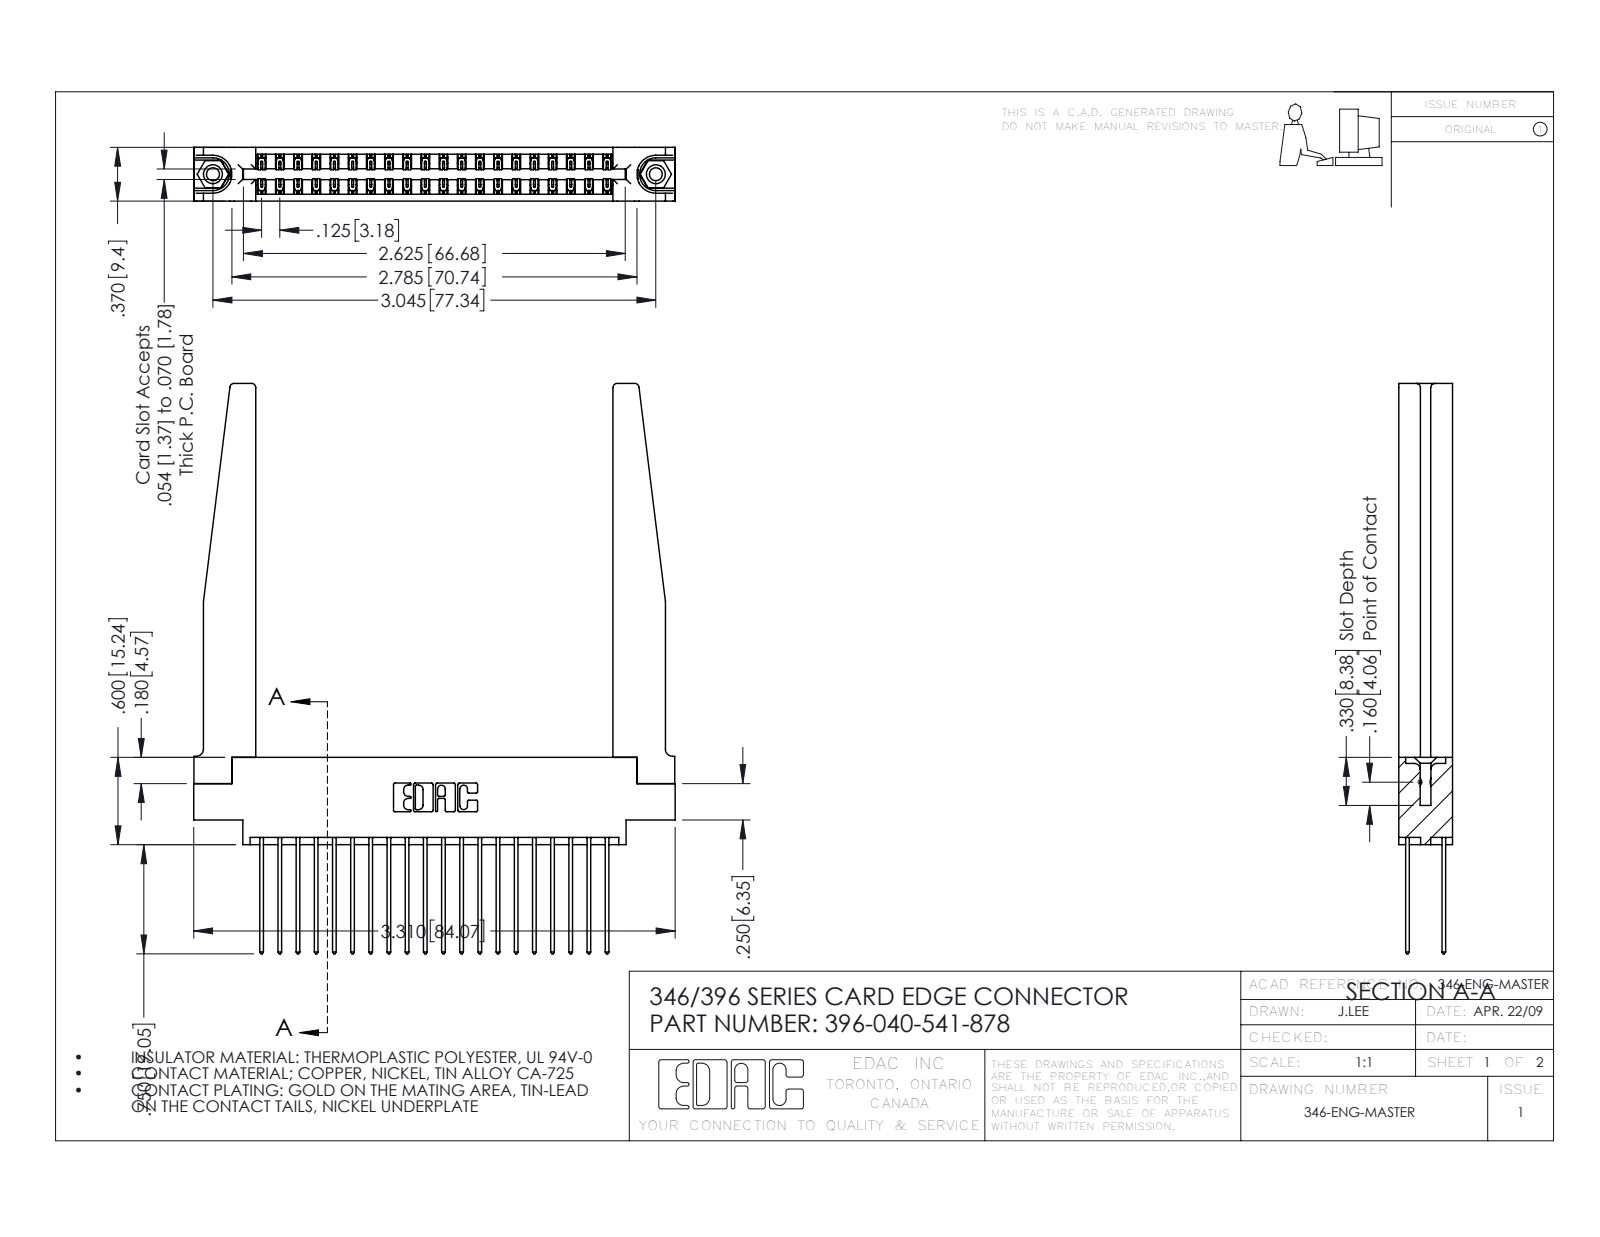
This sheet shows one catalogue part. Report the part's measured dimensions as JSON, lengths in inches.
{"part_name": "345-250-001_345-250-001-102; 346 Part_0.170 Offset - 0.156 Dia-TH; 346-220-078_345-220-078; 345-292-001_345-293-141 (+1 more)", "step_written_by": "SolidWorks 2016 (CONFIG_CONTROL_DESIGN)", "units": "inches", "bodies": {"solids": 45, "faces": 2440, "planar": 1622, "cylindrical": 766, "other": 52}, "overall_size": [3.92, 3.31, 0.37], "volume_in3": 0.916, "surface_area_in2": 28.84, "round_holes": [[0.089, 2], [0.125, 2], [0.156, 2], [0.064, 1]], "round_bosses_or_shafts": [[0.155, 2]], "partial_cylinders_radius": [[0.006, 60], [0.01, 40], [0.01, 22], [0.03, 8], [0.007, 6], [0.031, 6], [0.026, 3], [0.014, 2]], "face_to_face_distances": [0.37, 0.048, 0.322, 0.072, 0.25, 0.148, 0.15, 0.298, 0.025, 0.275], "hole_center_spacings": [0.246, 2.837, 3.045]}
